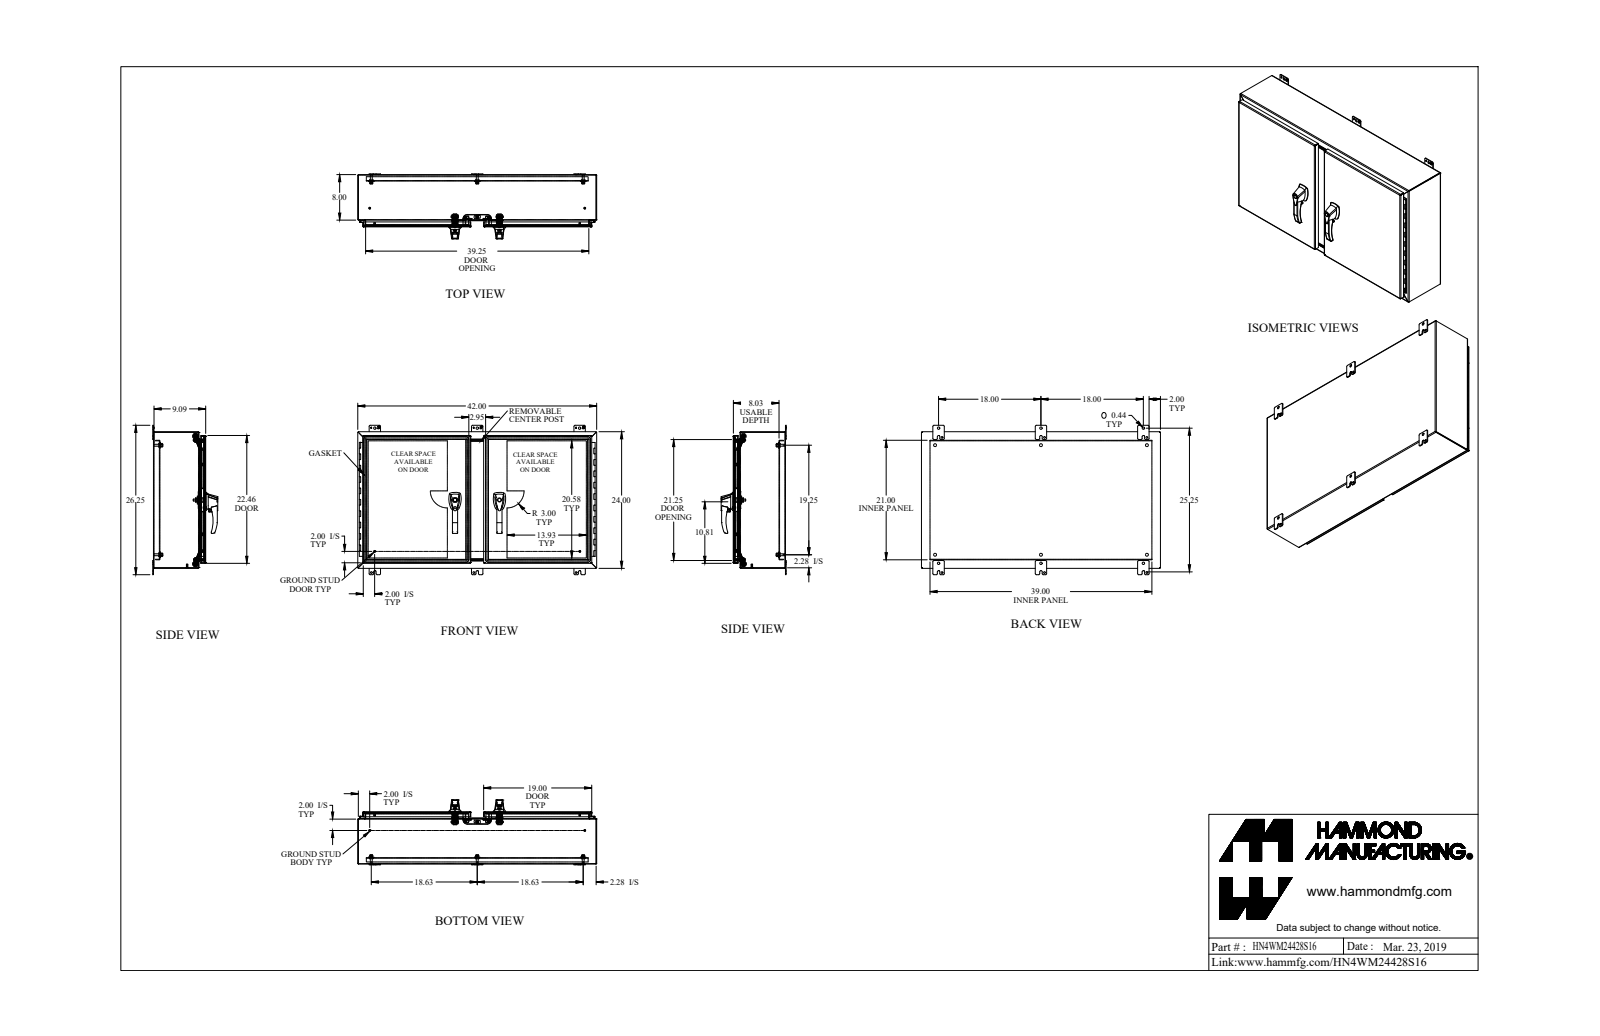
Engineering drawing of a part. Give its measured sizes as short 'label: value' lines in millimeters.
name: HN4WM24428S16
written by: SolidWorks 2018 (AUTOMOTIVE_DESIGN)
unit: mm
bodies: 112 solids, 2648 faces (1251 planar, 1117 cylindrical, 280 other)
size: 1066.8 × 666.8 × 290.2
volume: 7 815 000 mm³; area: 6 368 000 mm²
holes: 10× ⌀6.4, 9× ⌀8, 8× ⌀7.7, 6× ⌀5.1, 6× ⌀7.8, 6× ⌀11.3, 6× ⌀12.7, 4× ⌀6.5, 4× ⌀7.1, 4× ⌀7.1, 4× ⌀8, 4× ⌀9.9
bosses: 10× ⌀25.4, 6× ⌀16.5, 6× ⌀9.5, 6× ⌀8.4, 6× ⌀7.4, 4× ⌀19.1, 4× ⌀16, 4× ⌀15.9
rounds: 37× R3.2, 32× R0.5, 27× R4.8, 26× R6.4, 22× R1.5, 22× R12.7, 19× R1.2, 19× R3.6
face distances: 2.4, 26.2, 2.4, 230.9, 228.5, 233.3, 230.9, 28.6, 202.3, 204.7
hole spacings: 473.1, 446.7, 489, 680.3, 152.4, 622.4, 1030.4, 198.5
